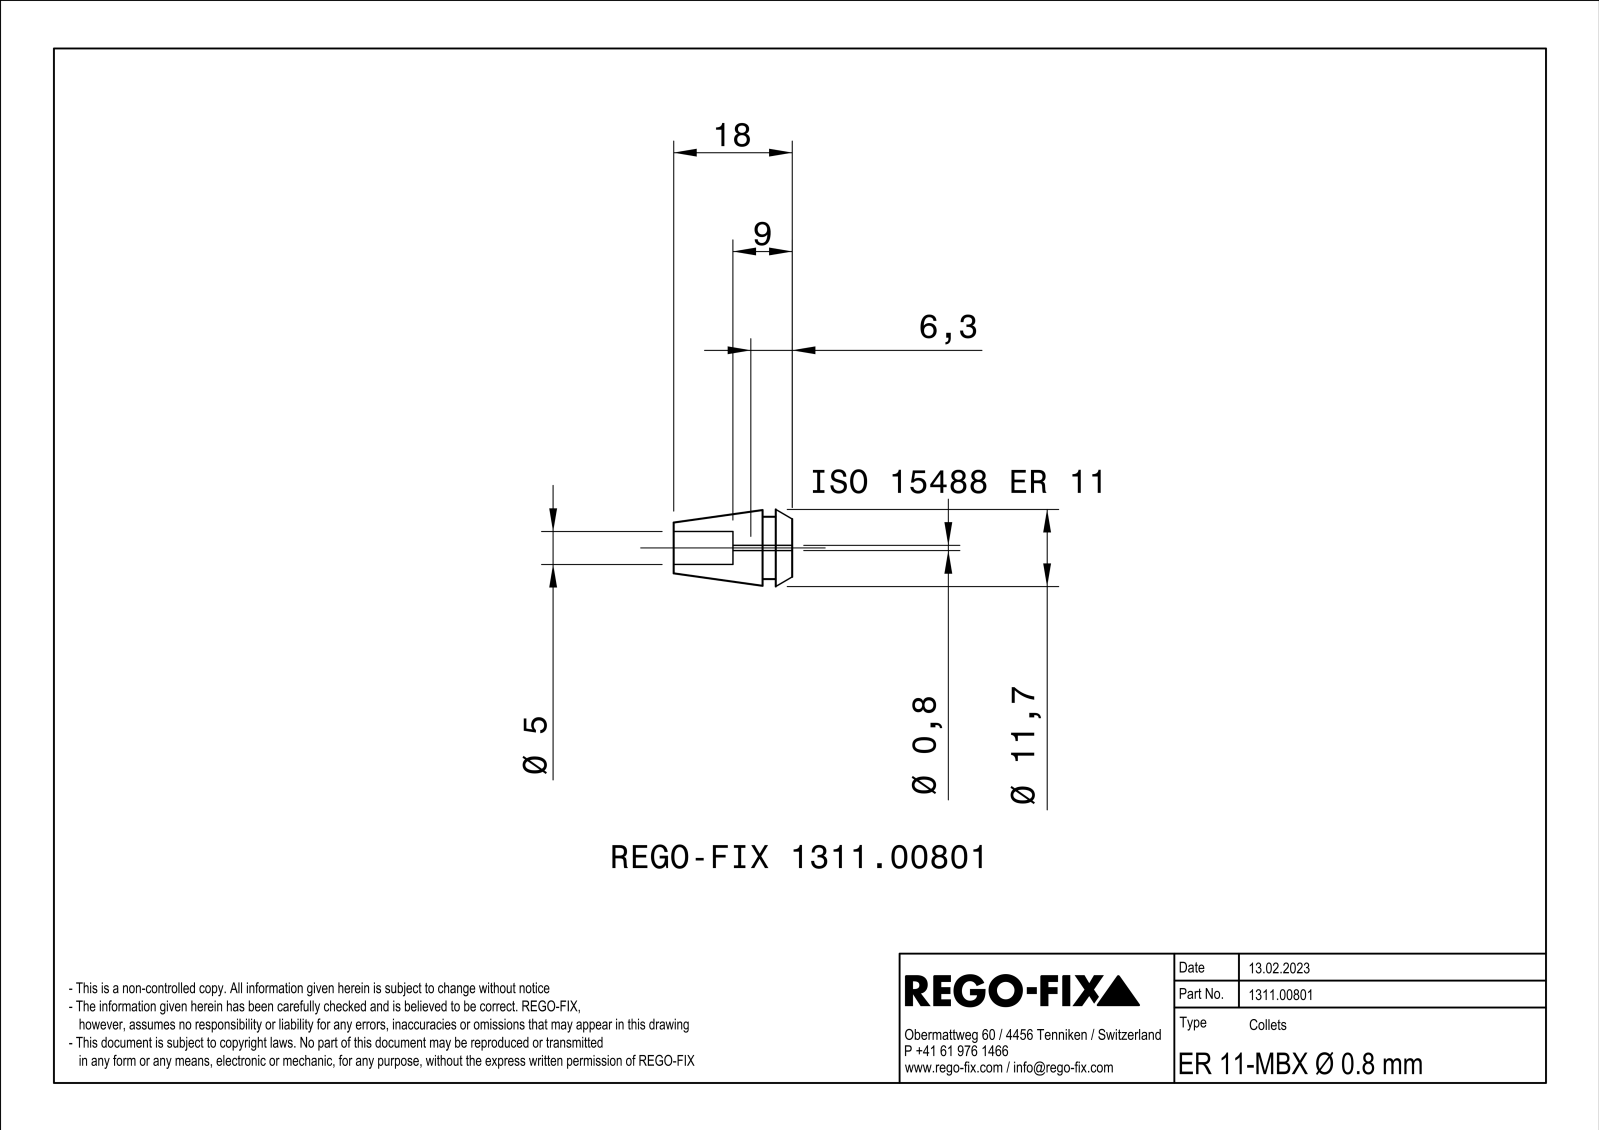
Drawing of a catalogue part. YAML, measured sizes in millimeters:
part_name: "NOCUT"
step_written_by: "SIEMENS PLM Software Solid Edge ST10 (AUTOMOTIVE_DESIGN)"
units: millimeters
bodies: {solids: 1, faces: 91, planar: 26, cylindrical: 19, other: 46}
overall_size: [18, 11.41, 11.39]
volume: 989
surface_area: 1253
round_holes:
  - {diameter: 1.5, count: 3}
  - {diameter: 5, count: 1}
round_bosses_or_shafts:
  - {diameter: 9.5, count: 1}
partial_cylinders:
  - {radius: 25, count: 3}
  - {radius: 0.4, count: 1}
face_to_face_distances: [0.8, 0.54, 4.5, 9, 18, 13.5, 2.5, 2, 15.5, 6.5]
hole_center_spacings: [1.7, 2.94]
